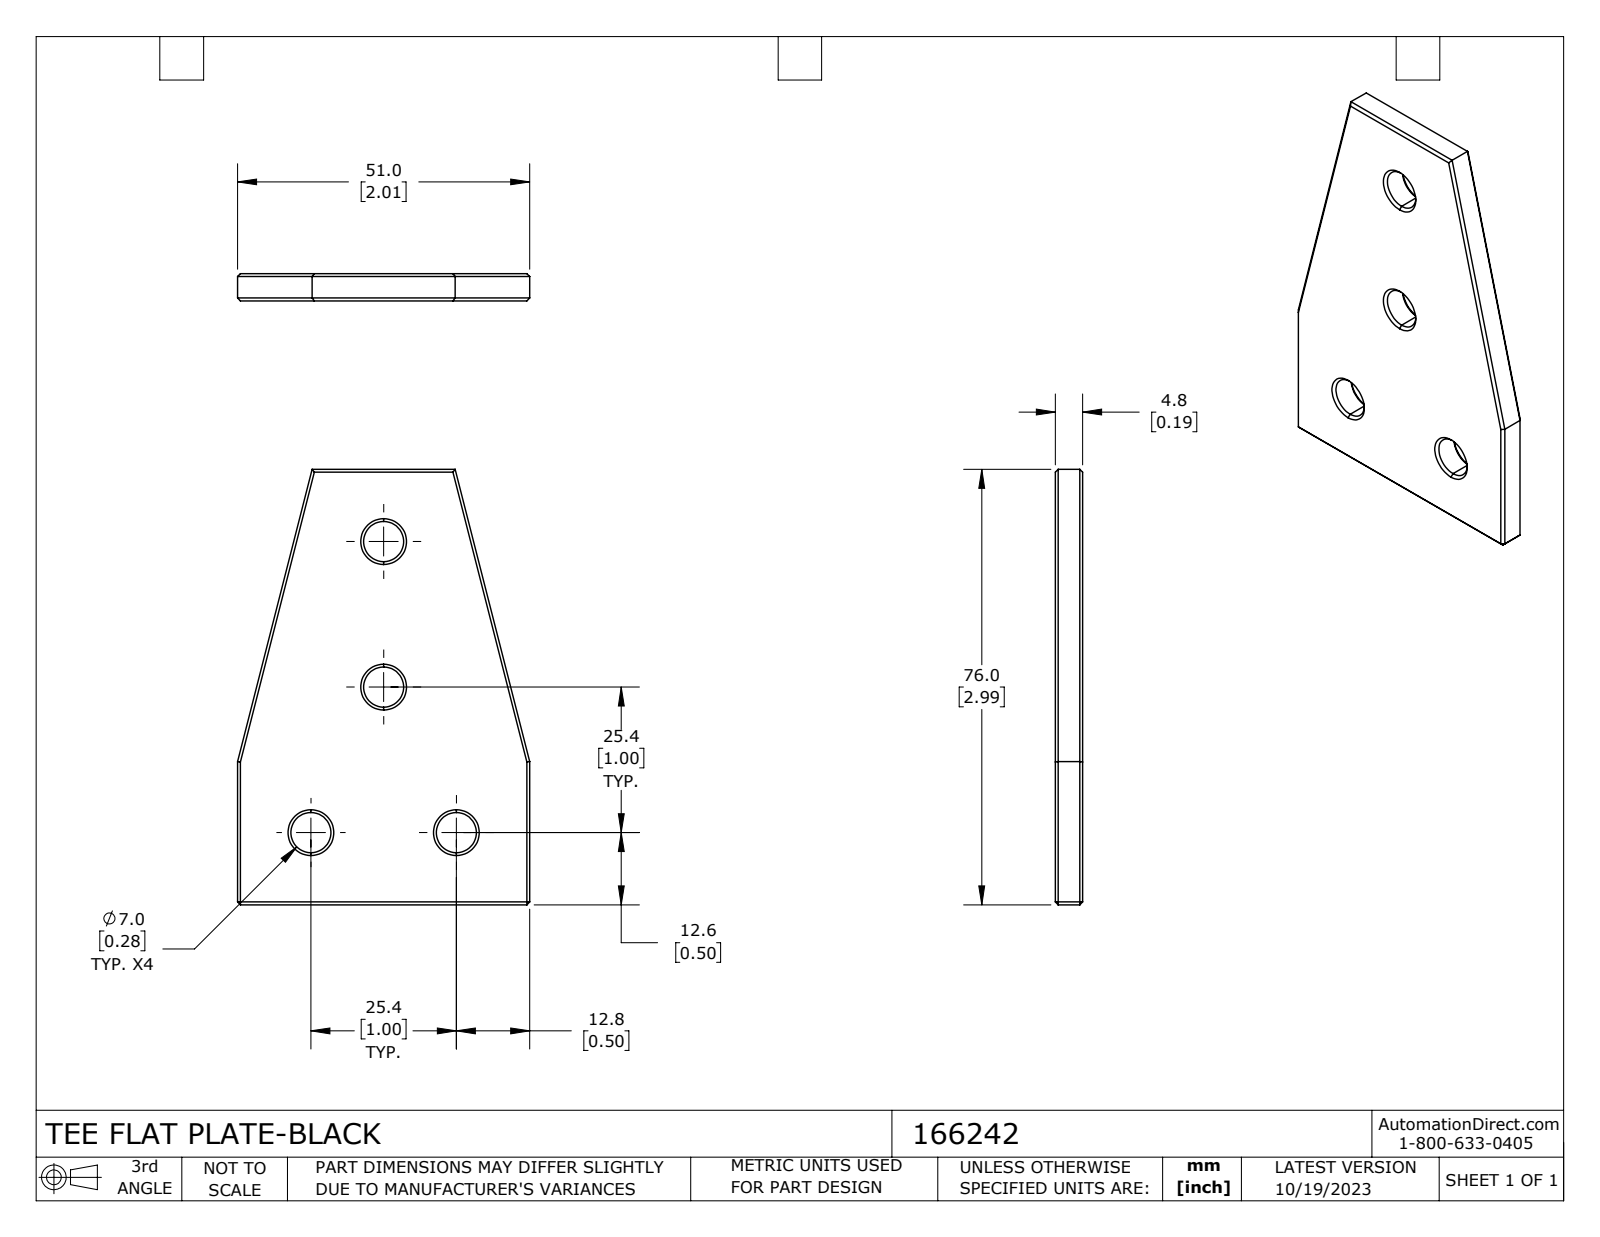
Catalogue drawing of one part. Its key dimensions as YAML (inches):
part_name: "166242"
step_written_by: "SolidWorks 2023 (CONFIG_CONTROL_DESIGN)"
units: inches
bodies: {solids: 1, faces: 50, planar: 26, cylindrical: 8, other: 16}
overall_size: [2.992, 2.008, 0.187]
volume: 0.884
surface_area: 11.55
round_holes:
  - {diameter: 0.276, count: 4}
face_to_face_distances: [0.187, 2.992, 2.008, 2.22, 1.524]
hole_center_spacings: [1, 1.118, 2.061]
